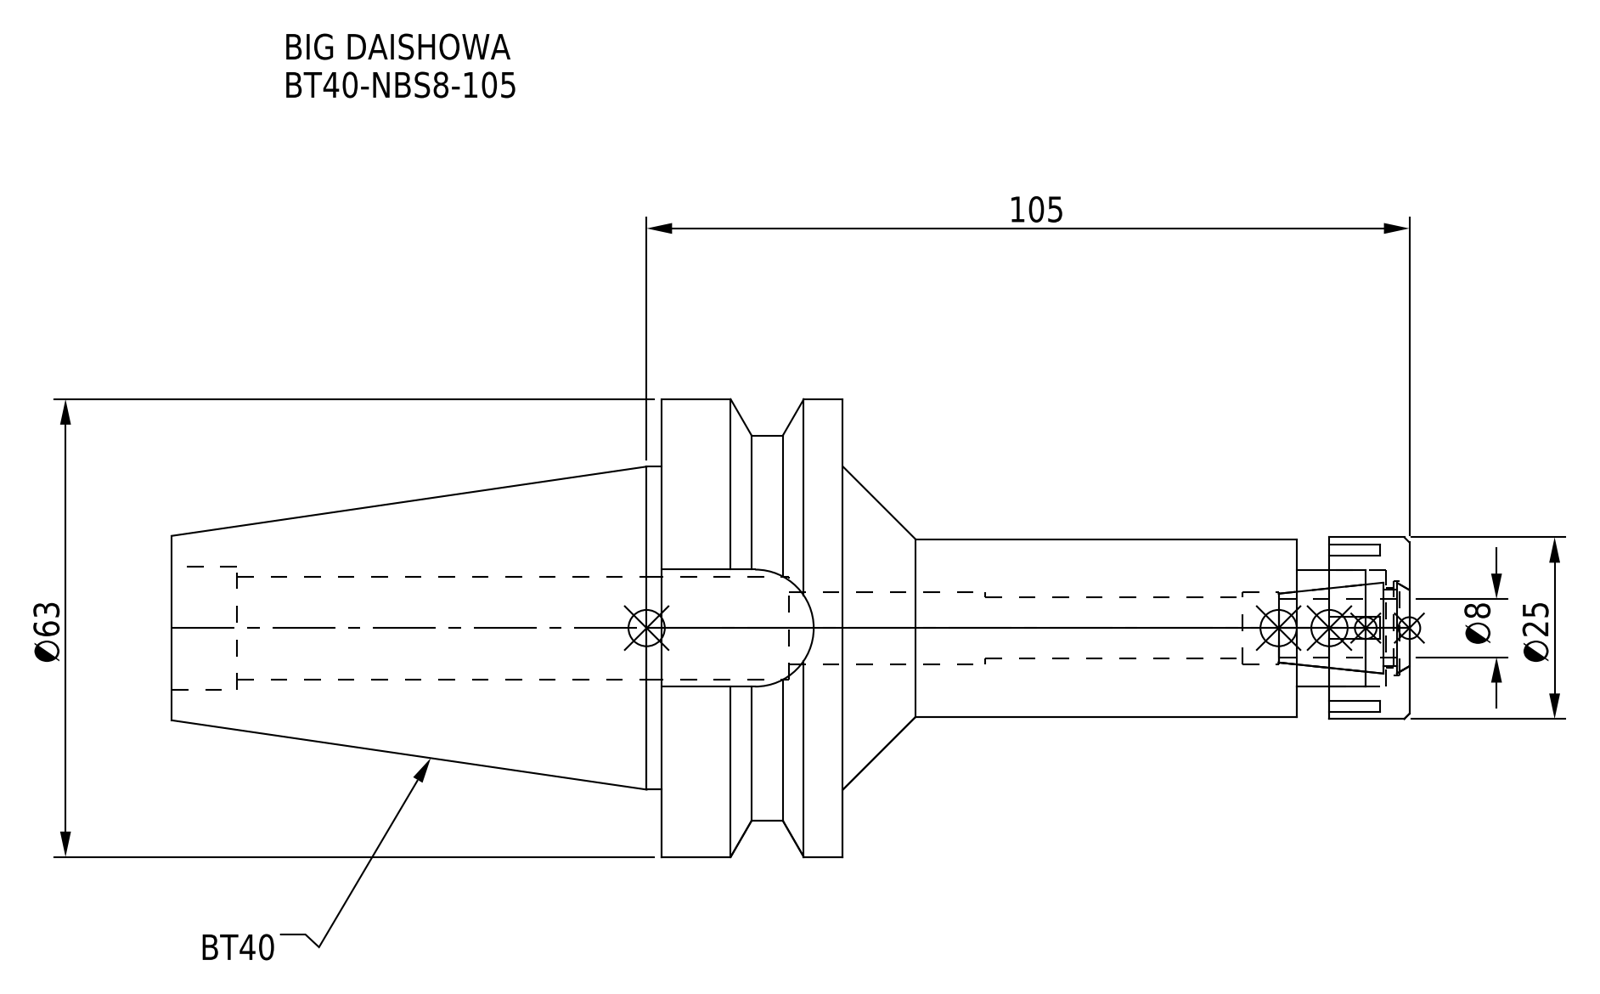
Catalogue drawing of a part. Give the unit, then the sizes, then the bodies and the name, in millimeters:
Units: millimetres
Overall size (bounding box): 170.4 × 63 × 63
Round holes (diameter × count): ⌀8.4 ×1, ⌀10 ×1, ⌀11 ×1, ⌀13 ×1, ⌀14.2 ×1, ⌀16 ×1, ⌀17 ×1
Round bosses / shafts (diameter × count): ⌀63 ×1, ⌀53 ×1, ⌀44.45 ×1, ⌀25 ×1, ⌀24.5 ×1
Partial cylindrical surfaces — rounded edges, fillets, slot ends (radius × count): R8.05 ×1
Main face-to-face distances: 25, 103, 78, 45, 67.4, 170.4, 92.4, 15.5, 62.5, 87.5
Volume: 154 203 mm³ · Surface area: 32 091 mm²
Bodies: 2 solids, 93 faces (45 planar, 34 cylindrical, 14 other)
Part name (STEP PRODUCT): BT40-NBS8-105_1.stp; BT40-NBS8-105-FreeParts; BT40NB08105-080_ASM.stp; DXF_TEMP_ASSY_ASM_4_ASM.stp (+3 more)
STEP written by: SolidWorks 2019 (CONFIG_CONTROL_DESIGN)
